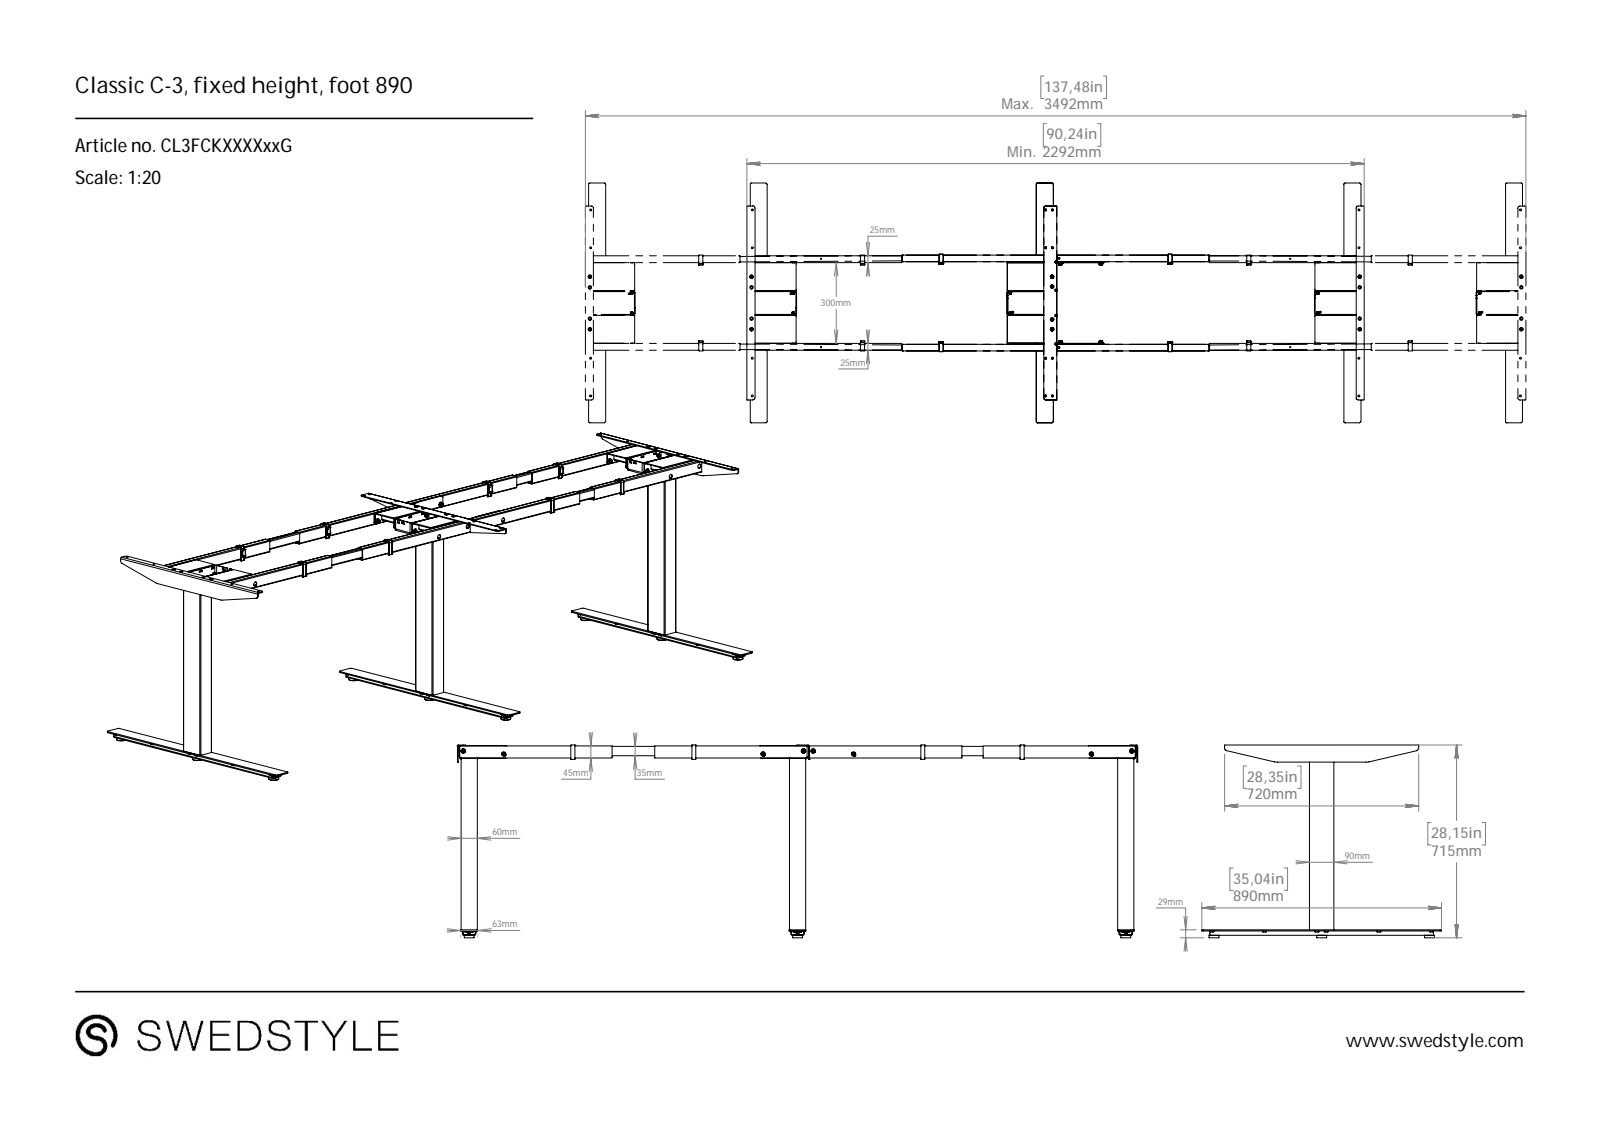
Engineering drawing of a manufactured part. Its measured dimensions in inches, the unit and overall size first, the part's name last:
Units: inches
Overall size (bounding box): 98.425 × 35.039 × 28.173
Round holes (diameter × count): ⌀0.63 ×17, ⌀0.276 ×16, ⌀0.197 ×6, ⌀0.213 ×5, ⌀0.165 ×4, ⌀0.295 ×4, ⌀0.236 ×3
Round bosses / shafts (diameter × count): ⌀0.459 ×6, ⌀0.386 ×5, ⌀0.315 ×3, ⌀0.613 ×1
Partial cylindrical surfaces — rounded edges, fillets, slot ends (radius × count): R0.098 ×92, R0.177 ×24, R0.197 ×21, R0.079 ×17, R0.118 ×16, R0.138 ×16, R0.276 ×13, R0.02 ×10
Main face-to-face distances: 0.118, 0.079, 0.787, 0.906, 12.913, 47.48, 0.098, 0.02, 0.039, 0.197
Hole centre spacings: 5.512, 21.654, 0.984, 4.114, 5.599, 8.681, 21.676, 23.228
Bodies: 0 solids, 1881 faces (823 planar, 576 cylindrical, 482 other)
Part name (STEP PRODUCT): Classic C-3, fixed height, foot 890_CL3FCKXXXXxxG
STEP written by: SolidWorks 2021 (CONFIG_CONTROL_DESIGN)
